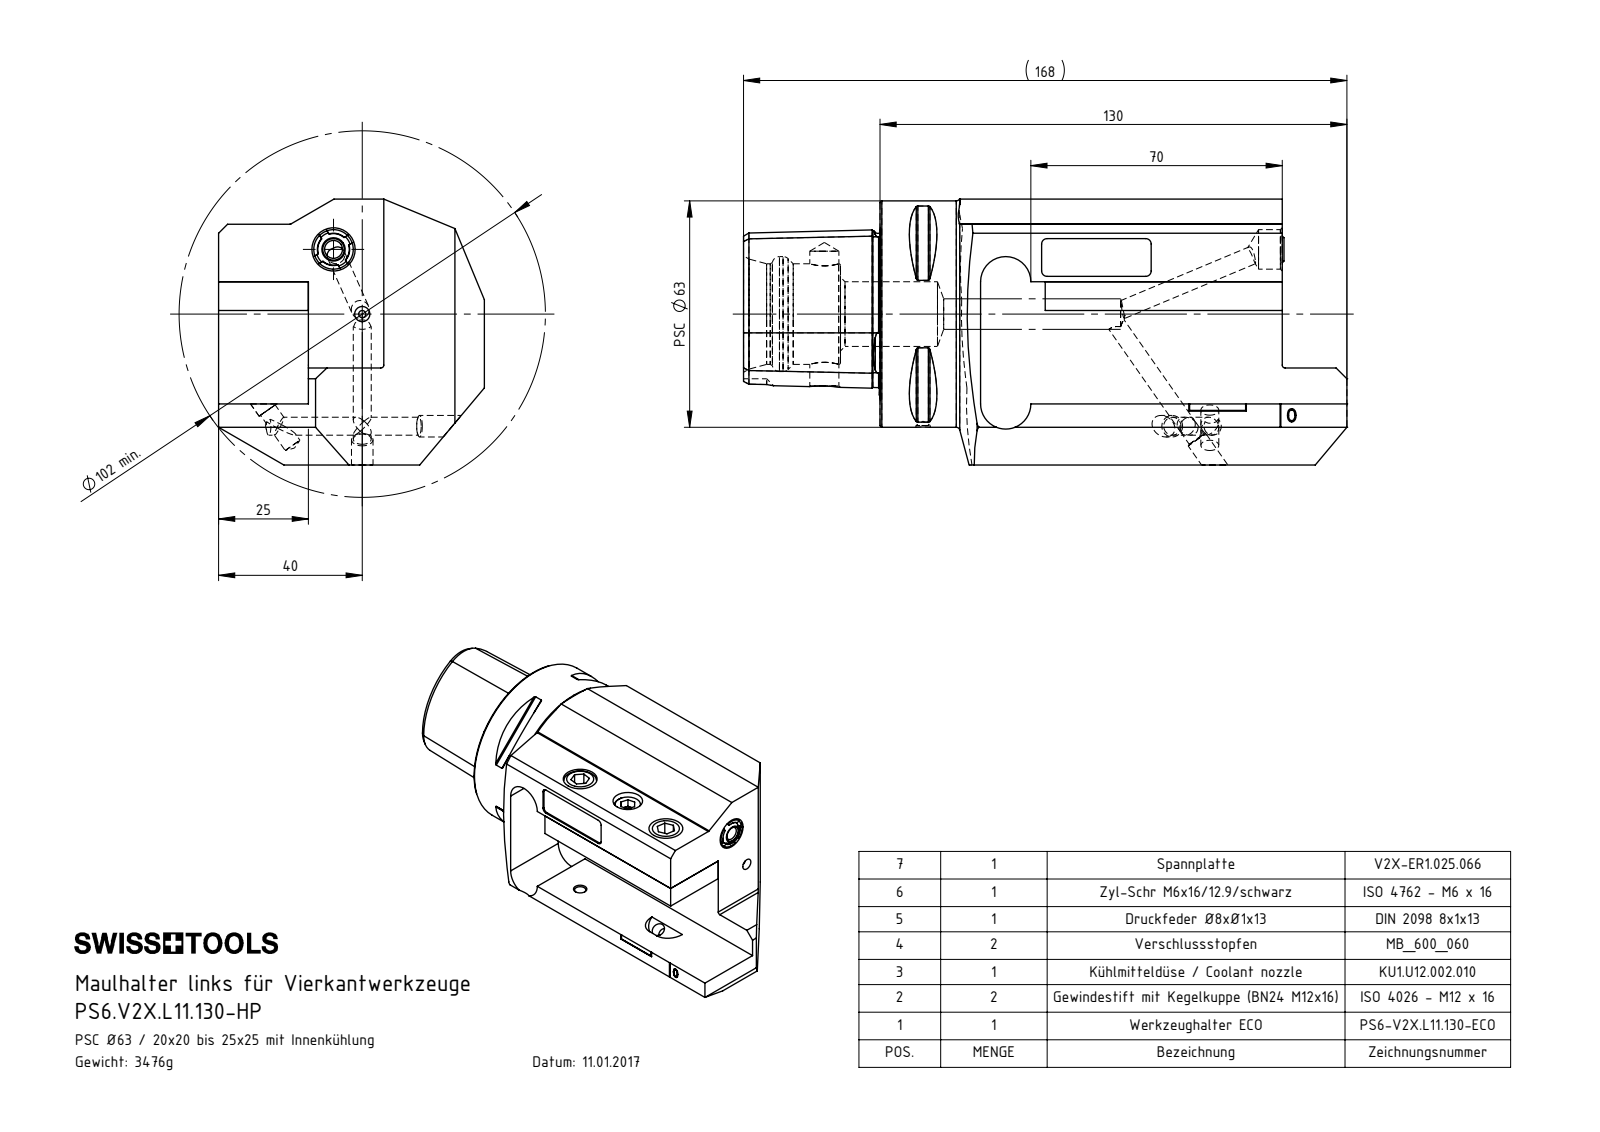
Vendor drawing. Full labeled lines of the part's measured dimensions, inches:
Part name (STEP PRODUCT): V2X-ER1.025.066_A; ISO 4762 - M6 x 16_PreviewCfg; 8x1x13_vorgespannt; S6-.2X.L11.130-ECO (+7 more)
STEP written by: SolidWorks 2022 (AUTOMOTIVE_DESIGN)
Units: inches
Bodies: 13 solids, 334 faces (127 planar, 77 cylindrical, 130 other)
Overall size (bounding box): 6.614 × 2.913 × 2.913
Volume: 27.02 in³ · Surface area: 100.7 in²
Round holes (diameter × count): ⌀0.197 ×8, ⌀0.236 ×2, ⌀0.402 ×2, ⌀0.433 ×2, ⌀0.079 ×1, ⌀0.157 ×1, ⌀0.165 ×1, ⌀0.268 ×1, ⌀0.319 ×1, ⌀0.335 ×1, ⌀0.394 ×1, ⌀0.709 ×1
Round bosses / shafts (diameter × count): ⌀0.472 ×3, ⌀0.236 ×3, ⌀2.48 ×1, ⌀0.394 ×1
Partial cylindrical surfaces — rounded edges, fillets, slot ends (radius × count): R0.02 ×8, R0.059 ×4, R0.236 ×3, R0.031 ×2, R0.276 ×2, R0.173 ×1
Main face-to-face distances: 2.008, 2.913, 0.669, 1.339, 0.984, 0.315, 1.024, 1.693, 0.63, 0.945
Hole centre spacings: 0.891, 0.776, 1.083, 1.772, 2.048, 2.779, 2.998, 3.642
